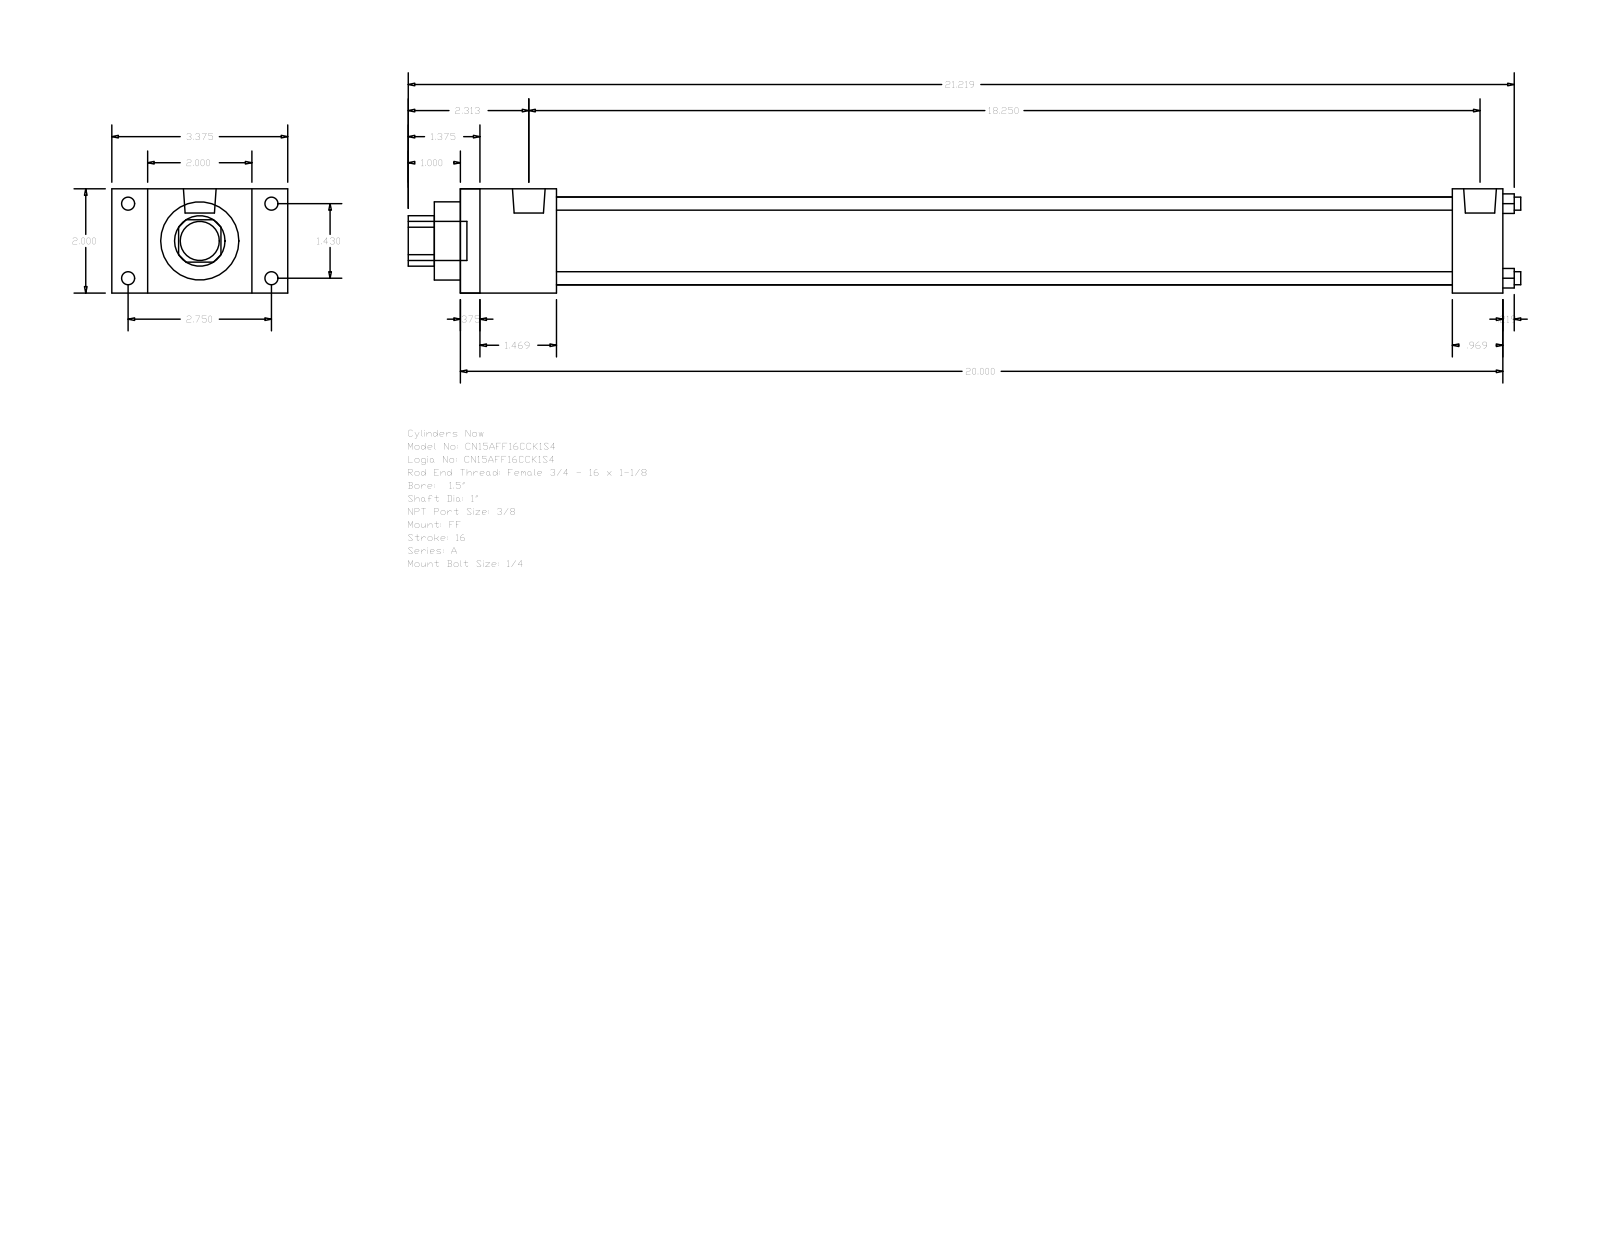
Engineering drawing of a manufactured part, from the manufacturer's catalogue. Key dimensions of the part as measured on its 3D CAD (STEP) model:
Part name (STEP PRODUCT): A_FF__0150_1
STEP written by: GSSL Pune (CONFIG_CONTROL_DESIGN)
Units: millimetres
Bodies: 0 solids, 92 faces (64 planar, 28 cylindrical, 0 other)
Overall size (bounding box): 542.13 × 85.72 × 50.8
Round holes (diameter × count): ⌀6.35 ×4, ⌀25.4 ×1, ⌀38.1 ×1, ⌀42.93 ×1
Round bosses / shafts (diameter × count): ⌀6.35 ×4, ⌀5.56 ×4, ⌀15.93 ×2, ⌀19.05 ×1
Partial cylindrical surfaces — rounded edges, fillets, slot ends (radius × count): R12.29 ×1
Main face-to-face distances: 50.8, 508, 9.52, 498.48, 46.83, 483.39, 37.31, 473.87, 436.56, 461.17
Hole centre spacings: 25.68, 36.32, 51.36
